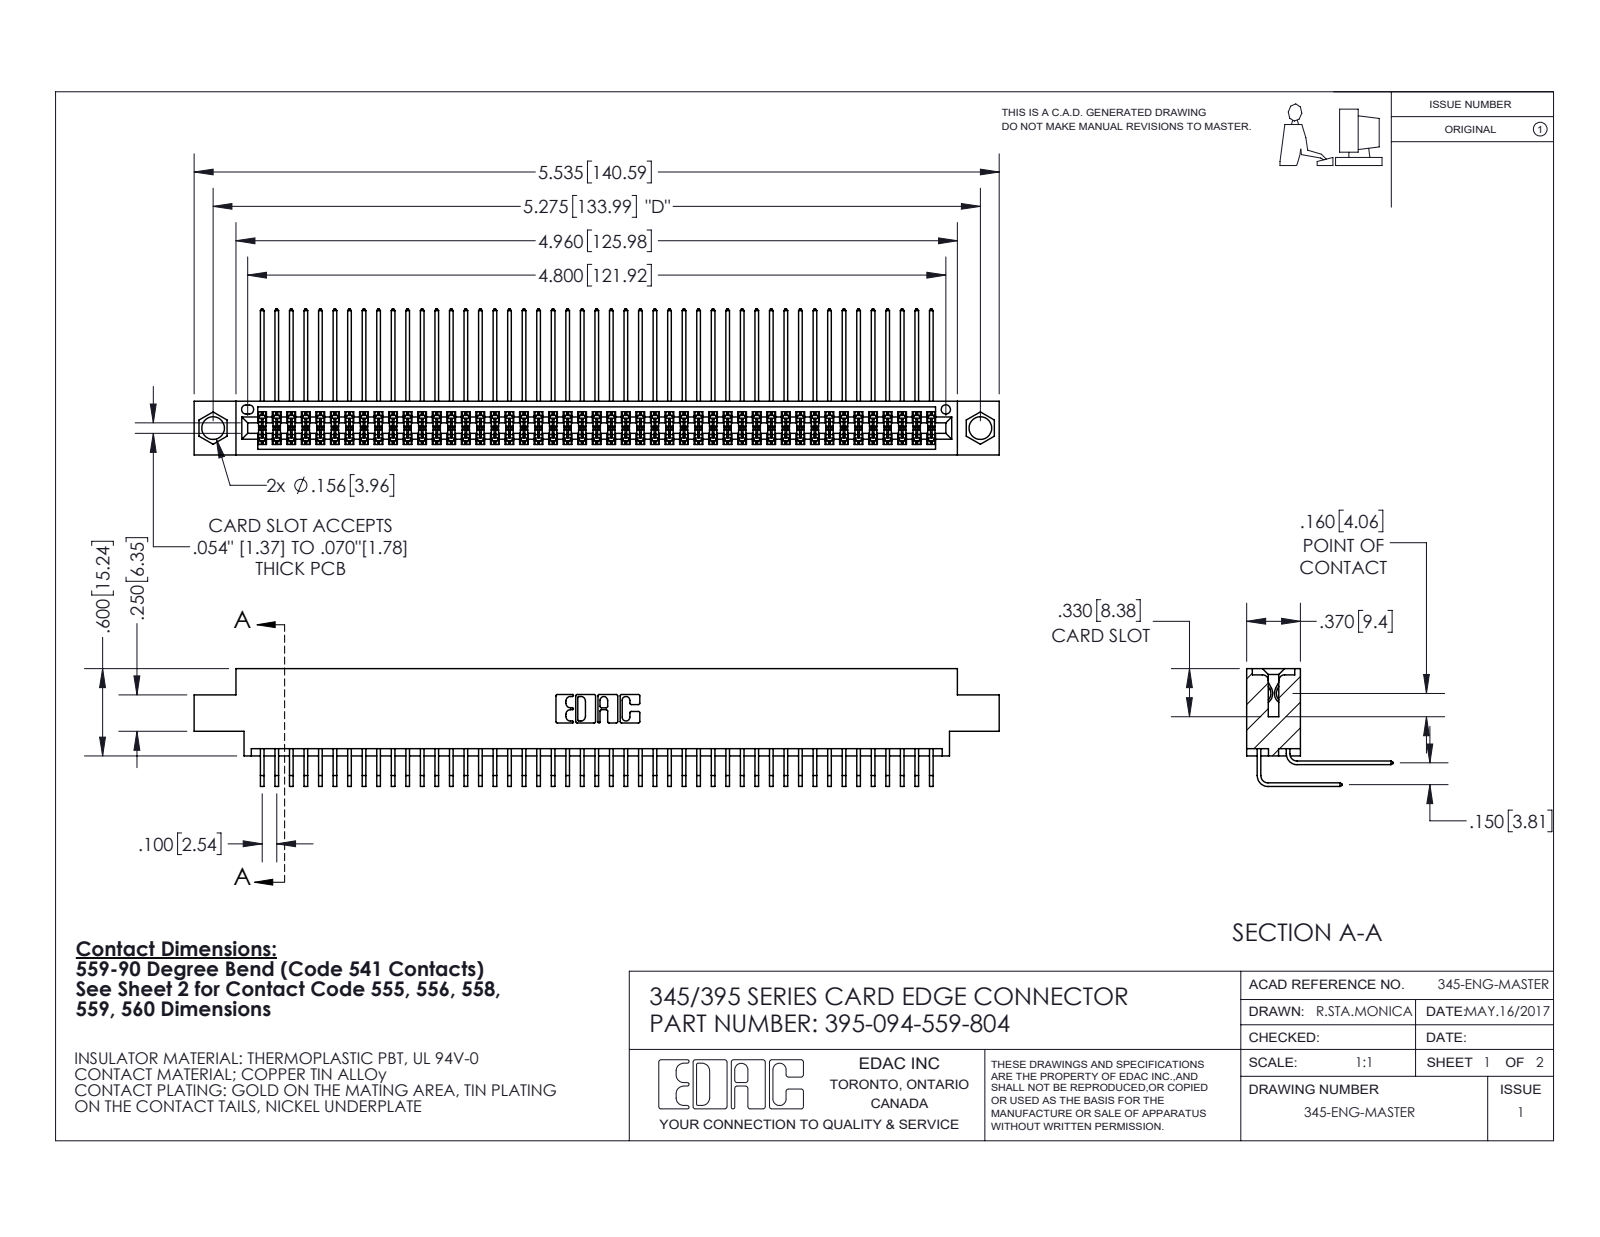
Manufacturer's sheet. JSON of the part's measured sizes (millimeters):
{"part_name": "345-292-001_559 Tail - 2; 395-094-559-804; 345-292-001_558 559 Tail - 1; 345 Part_0.170 Offset - 0.156 Dia-TI", "step_written_by": "SolidWorks 2020 (CONFIG_CONTROL_DESIGN)", "units": "millimeters", "bodies": {"solids": 95, "faces": 5032, "planar": 3388, "cylindrical": 1644, "other": 0}, "overall_size": [140.6, 25.5, 20.5], "volume_mm3": 14000, "surface_area_mm2": 23370, "round_holes": [[4, 2], [1.6, 1]], "partial_cylinders_radius": [[0.2, 188], [0.3, 22], [0.2, 6], [0.8, 6], [0.7, 3], [0.4, 2], [0.5, 2], [0.6, 2]], "face_to_face_distances": [1.8, 7.6, 9.4, 5.1, 2.5, 6.9, 0.6, 5.7, 4.4, 3.8], "hole_center_spacings": [6.9, 128, 134]}
